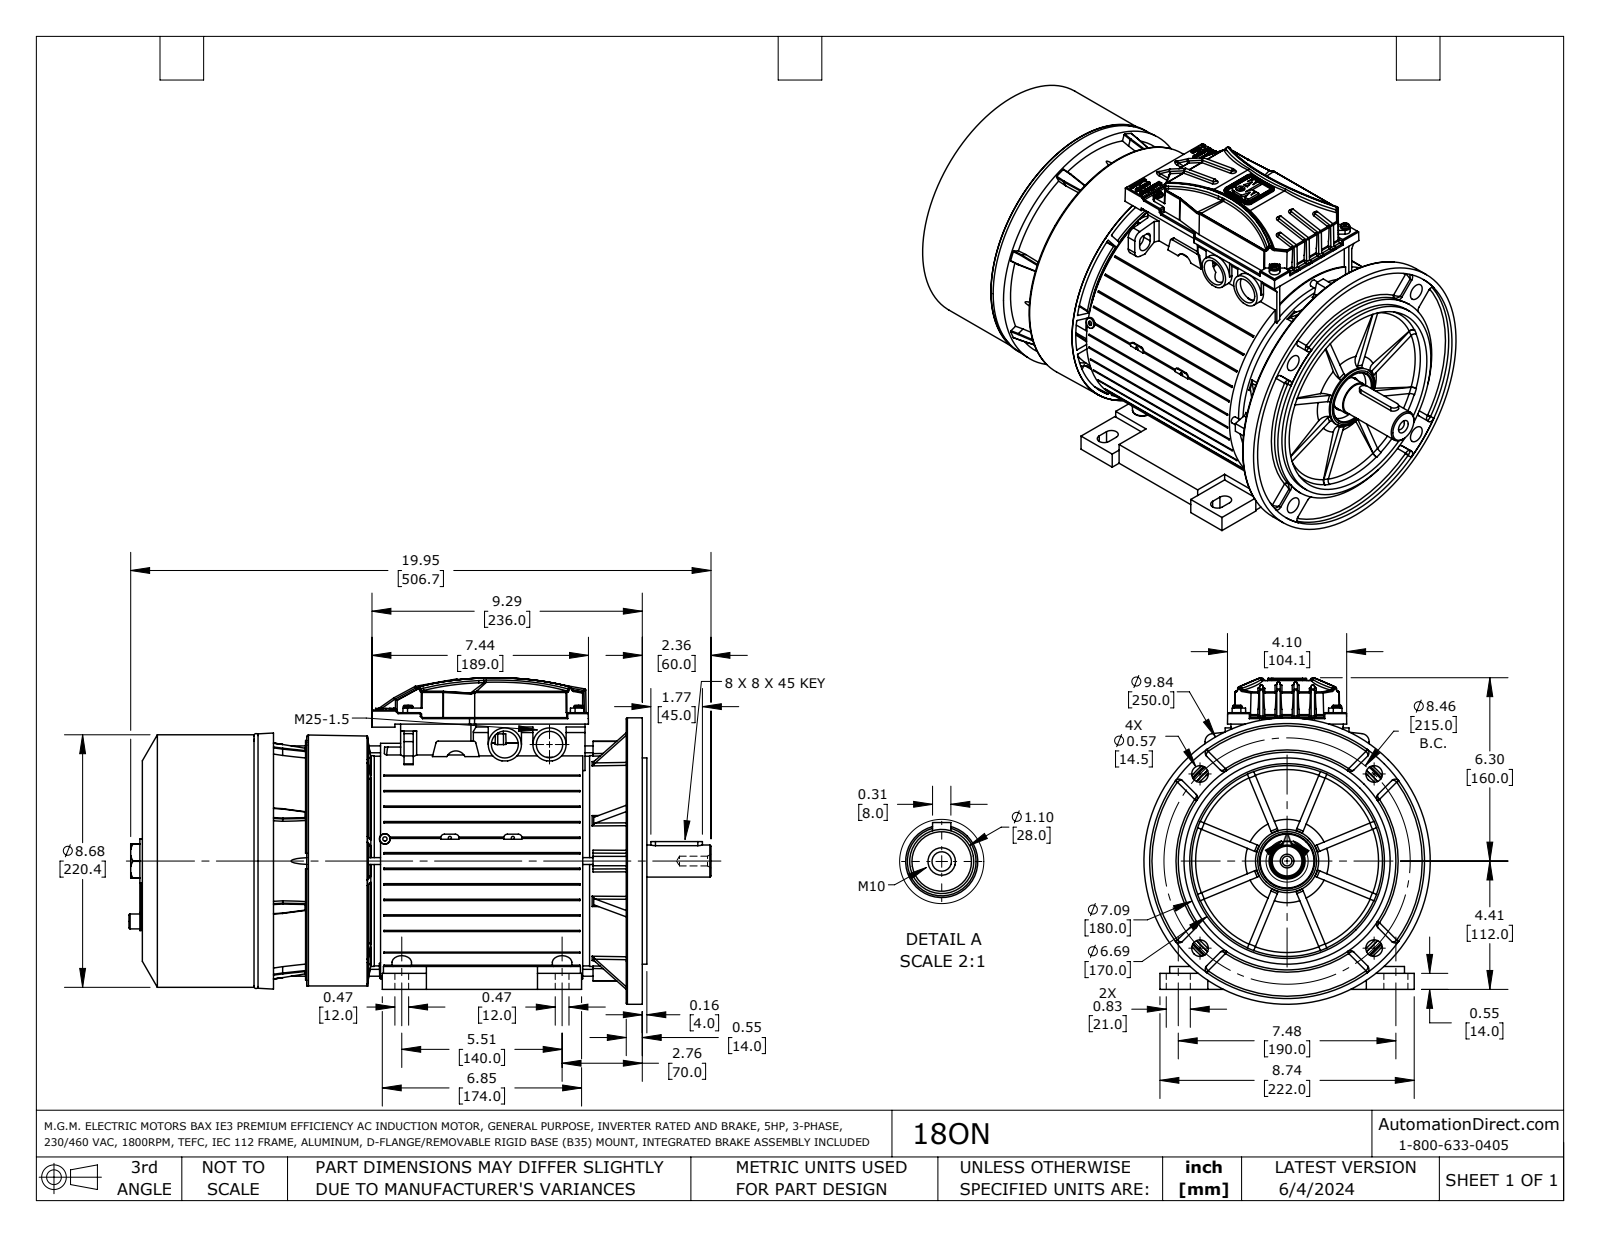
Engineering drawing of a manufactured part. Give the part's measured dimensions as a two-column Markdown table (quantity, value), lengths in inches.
| quantity | value |
| --- | --- |
| part name | 18ON |
| STEP written by | SolidWorks 2021 (AUTOMOTIVE_DESIGN) |
| units | inches |
| bodies | 12 solids, 3535 faces (1308 planar, 789 cylindrical, 1438 other) |
| overall size | 20.007 × 11.221 × 9.843 |
| volume | 789.2 in³ |
| surface area | 1 639 in² |
| round holes (diameter × count) | 0.13 × 11, 0.098 × 5, 0.335 × 5, 0.15 × 4, 0.177 × 4, 0.197 × 4, 0.531 × 4, 0.571 × 4, 0.148 × 3, 0.106 × 2, 0.118 × 2, 0.165 × 2 |
| round bosses / shafts (diameter × count) | 0.315 × 8, 0.138 × 6, 0.522 × 4, 0.236 × 4, 1.142 × 2, 9.843 × 1, 8.677 × 1, 8.563 × 1 |
| partial cylindrical surfaces (radius × count) | 0.008 × 56, 0.059 × 47, 0.039 × 38, 0.157 × 38, 0.004 × 24, 0.02 × 22, 0.033 × 16, 0.079 × 9 |
| main face-to-face distances | 0.236, 9.665, 15.374, 5.709, 7.639, 2.027, 7.735, 1.811, 11.063, 0.787 |
| hole center spacings | 0.472, 3.11, 7.458, 0.818, 3.438, 3.626, 3.778, 3.839 |
